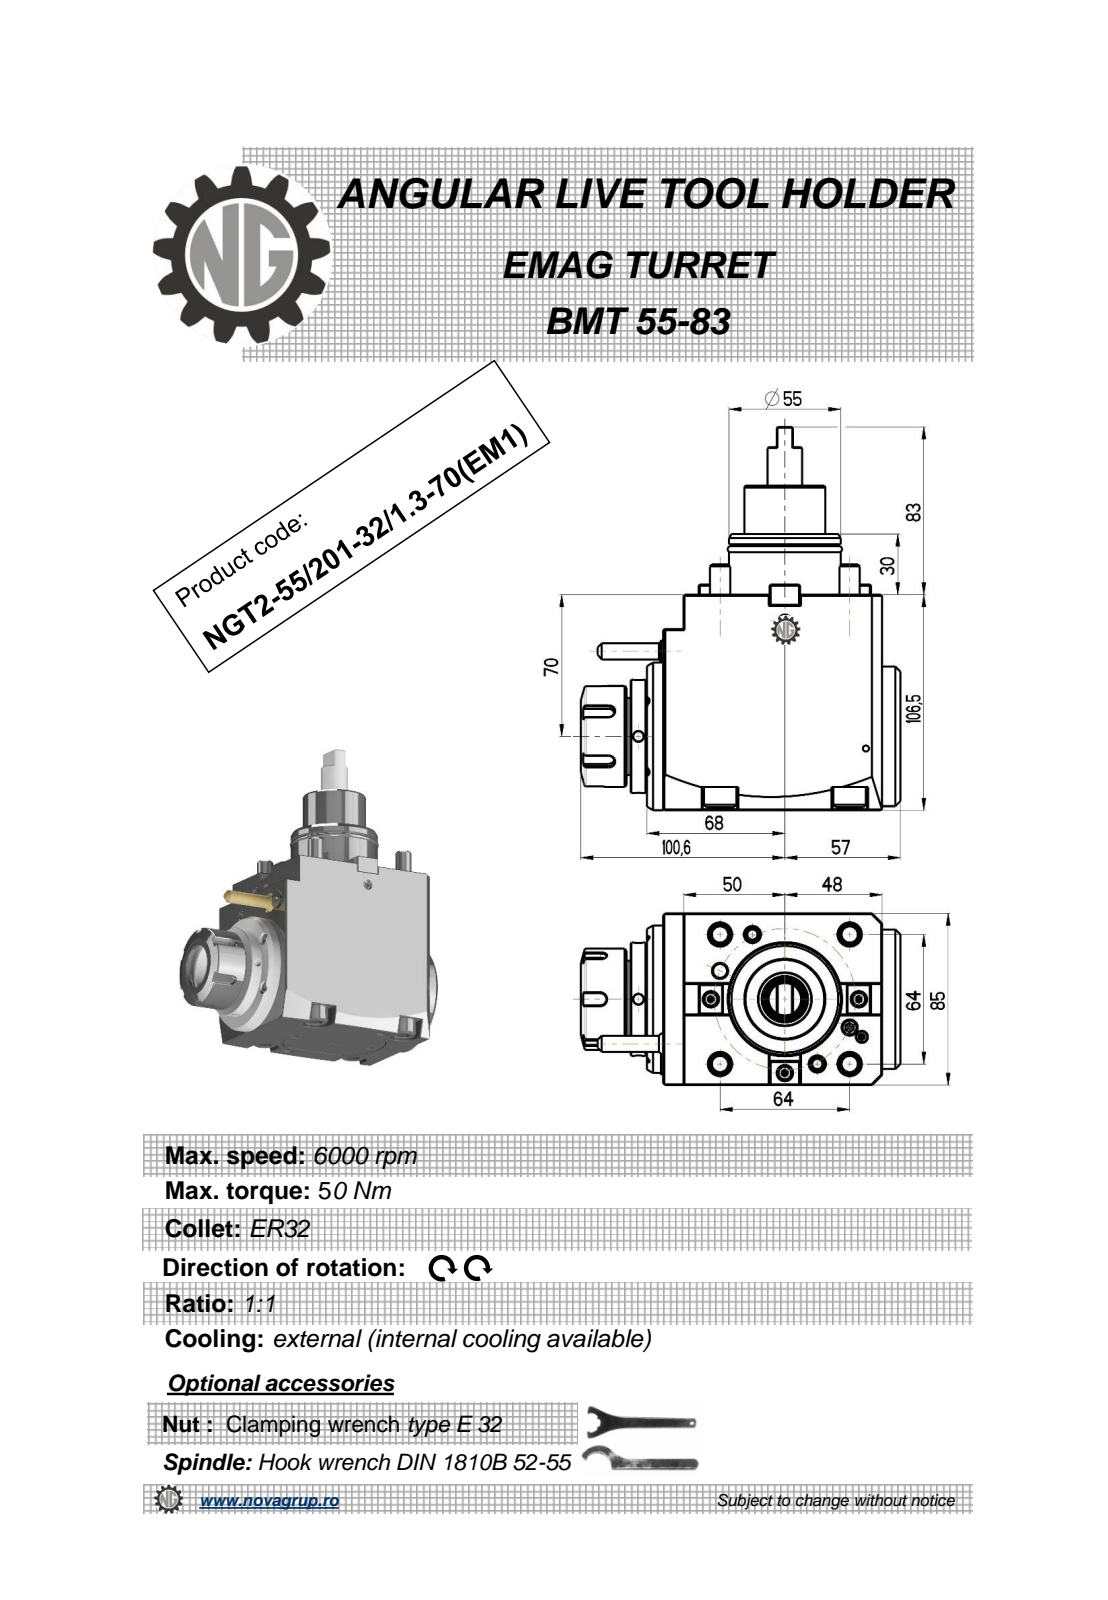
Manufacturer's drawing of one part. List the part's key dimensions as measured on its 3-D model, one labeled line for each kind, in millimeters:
Part name (STEP PRODUCT): NGT2_55_201_32_1_3_70_EM1
STEP written by: PRO/ENGINEER BY PARAMETRIC TECHNOLOGY CORPORATION, 2010280 (CONFIG_CONTROL_DESIGN)
Units: millimetres
Bodies: 2 solids, 472 faces (228 planar, 111 cylindrical, 133 other)
Overall size (bounding box): 189.5 × 157.6 × 85
Volume: 1 180 000 mm³ · Surface area: 103 724 mm²
Round holes (diameter × count): ⌀5 ×3, ⌀6.8 ×2, ⌀3 ×1, ⌀12 ×1, ⌀27 ×1
Round bosses / shafts (diameter × count): ⌀16 ×4, ⌀10 ×4, ⌀50 ×2, ⌀73 ×1, ⌀69 ×1, ⌀56 ×1, ⌀55 ×1, ⌀43.4 ×1
Partial cylindrical surfaces — rounded edges, fillets, slot ends (radius × count): R0.32 ×20, R0.22 ×6, R3 ×5, R8.5 ×4, R0.8 ×2, R480 ×2
Main face-to-face distances: 85, 106.5, 9, 8, 125, 108, 117, 116, 10, 18
Hole centre spacings: 42.62, 47.41, 69.86, 105.19
